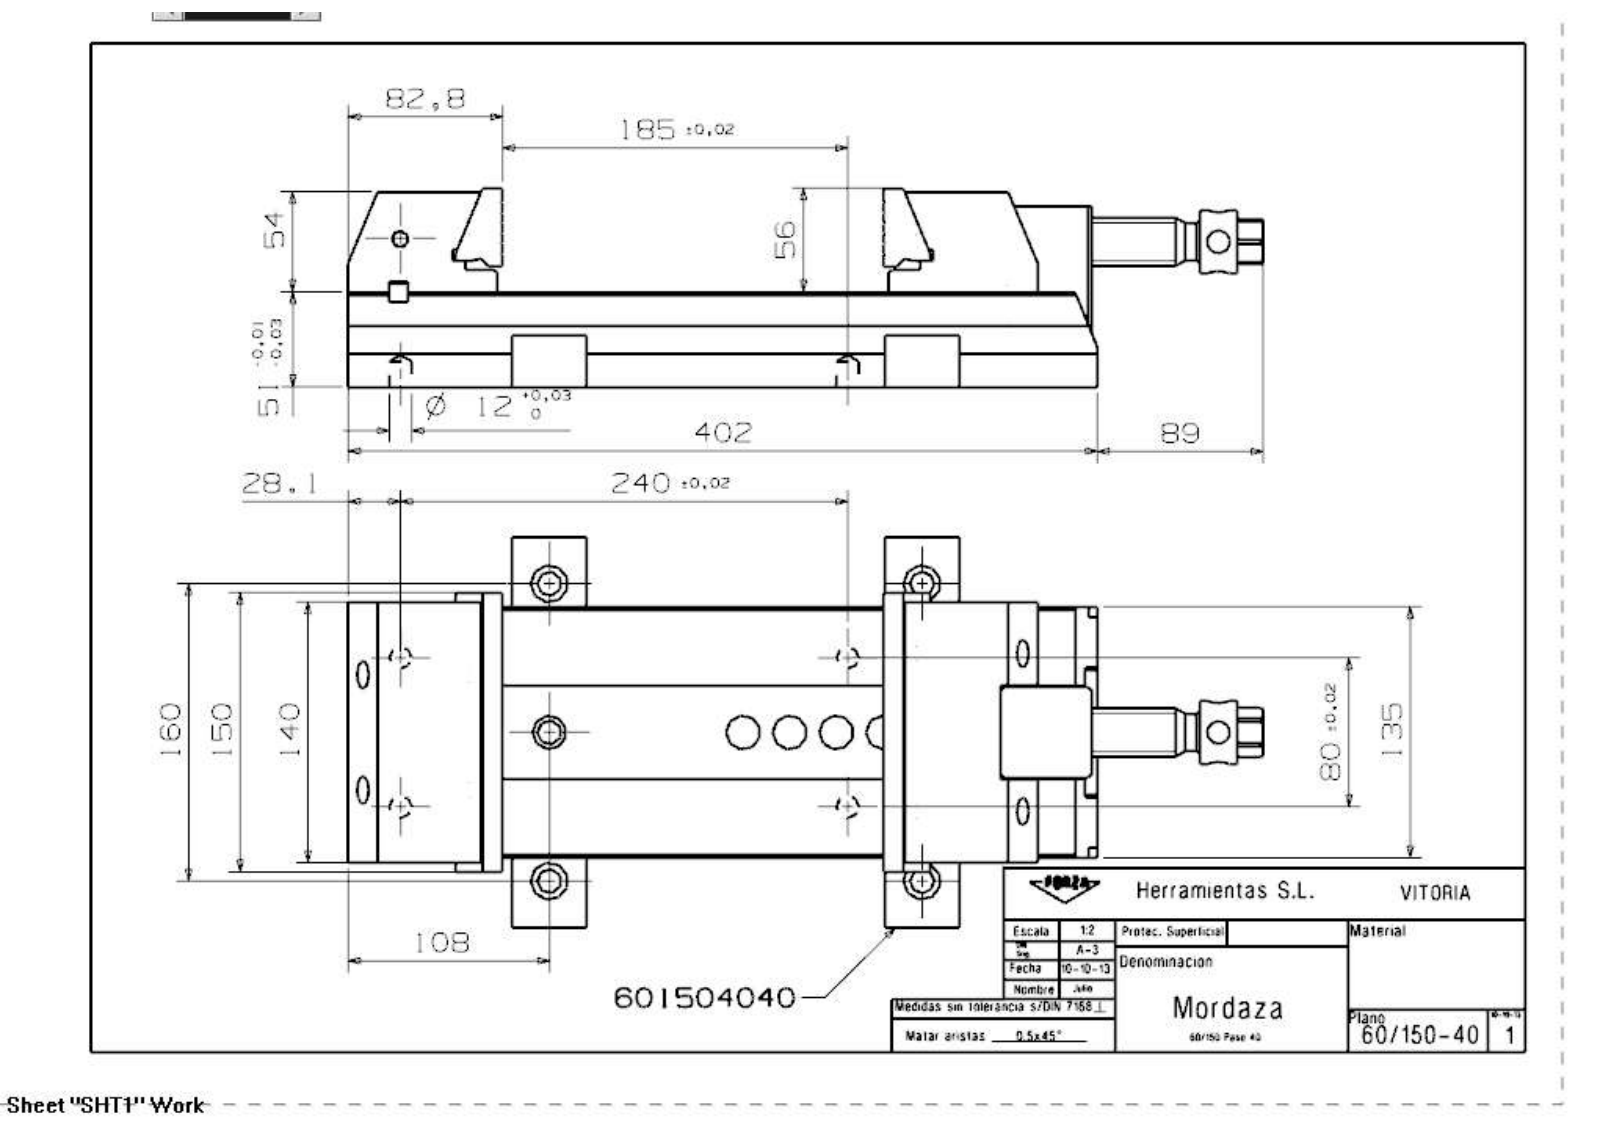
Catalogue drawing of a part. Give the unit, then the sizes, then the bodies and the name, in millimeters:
Units: millimetres
Overall size (bounding box): 491 × 210 × 107
Round holes (diameter × count): ⌀13 ×9, ⌀12 ×6, ⌀15 ×6, ⌀20 ×5, ⌀6.99 ×4, ⌀8.5 ×4, ⌀8.78 ×4, ⌀10 ×4, ⌀10.58 ×4, ⌀19 ×4, ⌀12.38 ×2, ⌀22 ×2
Round bosses / shafts (diameter × count): ⌀34 ×1, ⌀33.8 ×1, ⌀26 ×1, ⌀20 ×1, ⌀16.5 ×1
Partial cylindrical surfaces — rounded edges, fillets, slot ends (radius × count): R1.5 ×4, R20 ×4, R1.6 ×2, R5.5 ×2, R6 ×2, R4 ×1, R9 ×1, R10.5 ×1
Main face-to-face distances: 51, 105, 19.3, 31.7, 35, 129.5, 27, 85.7, 54, 1.6
Hole centre spacings: 80, 95.18, 11.5, 73.5, 85, 89.35, 165.02, 11.56
Volume: 3 329 000 mm³ · Surface area: 482 798 mm²
Bodies: 16 solids, 465 faces (312 planar, 100 cylindrical, 53 other)
Part name (STEP PRODUCT): 60_150_Mordaza
STEP written by: SIEMENS PLM Software NX 7.5 (CONFIG_CONTROL_DESIGN)
